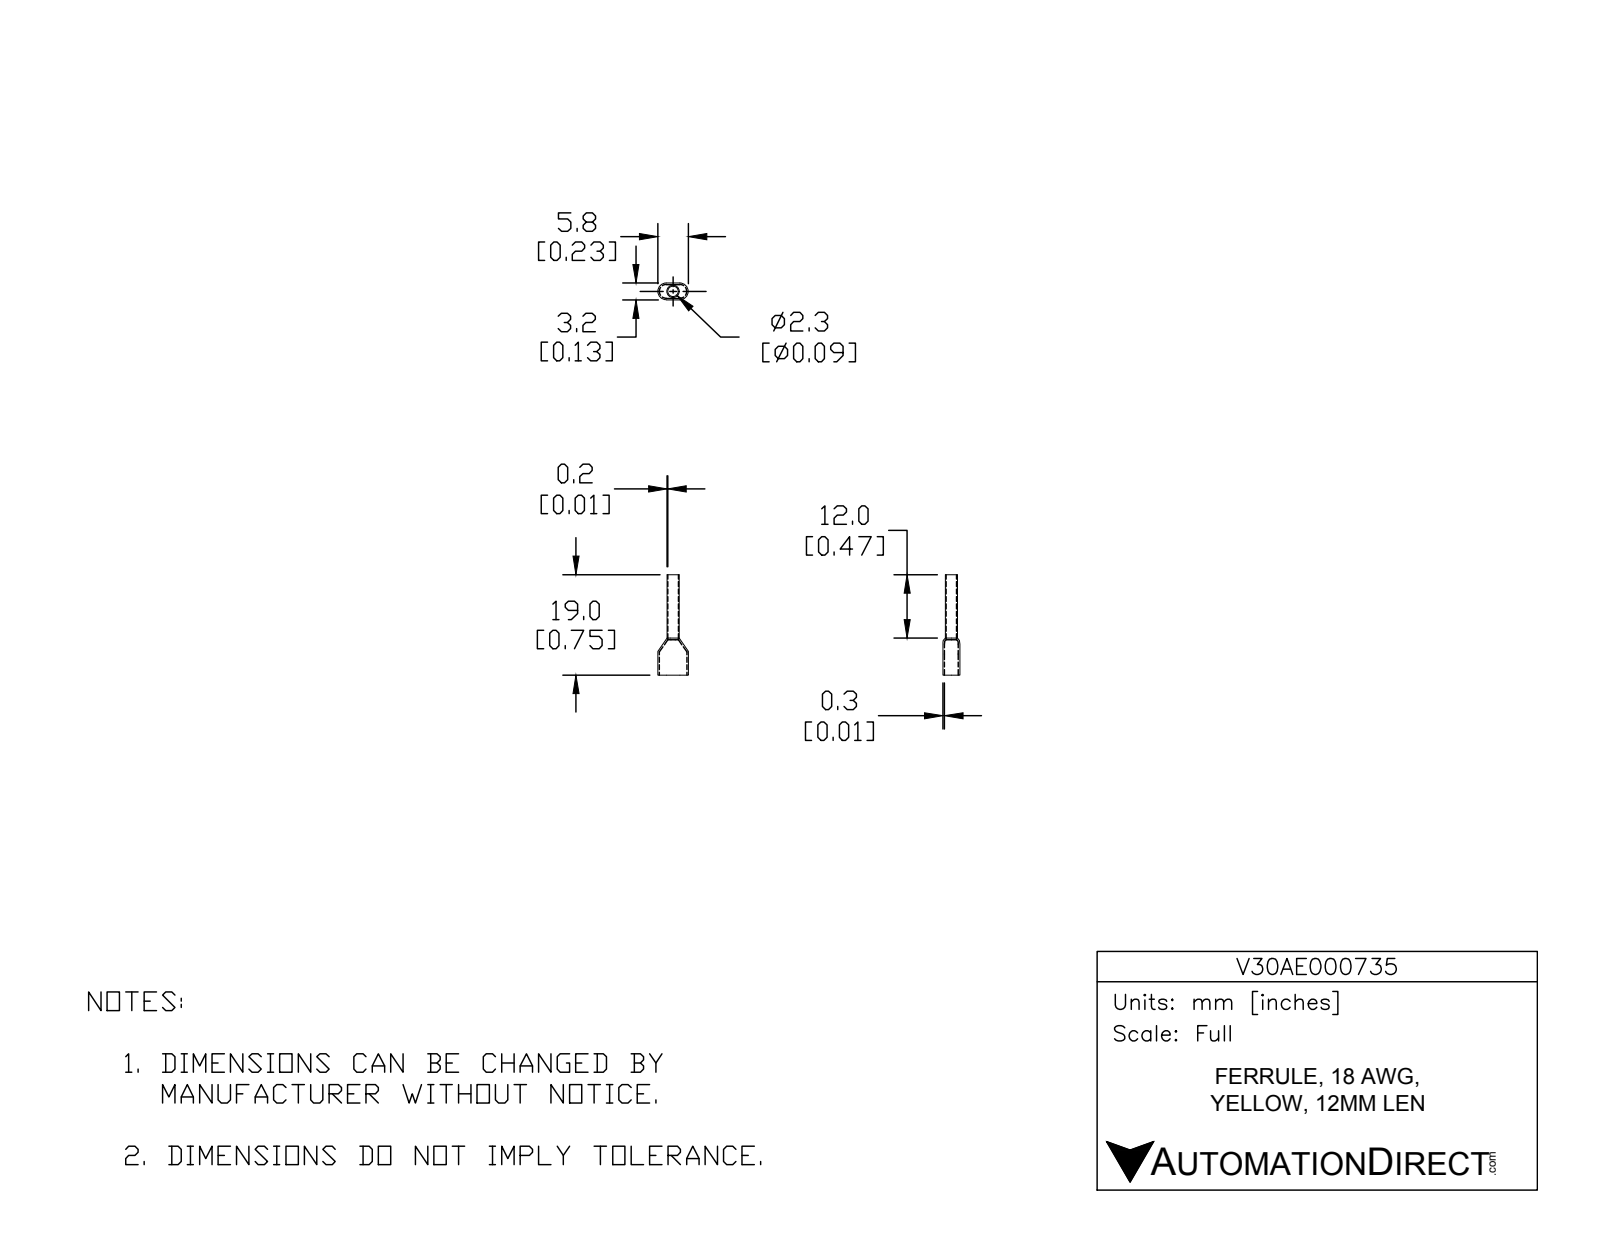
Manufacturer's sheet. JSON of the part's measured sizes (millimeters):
{"part_name": "V30AE000735", "step_written_by": "SolidWorks 2017 (AUTOMOTIVE_DESIGN)", "units": "millimeters", "bodies": {"solids": 2, "faces": 36, "planar": 14, "cylindrical": 22, "other": 0}, "overall_size": [19, 5.8, 3.2], "volume_mm3": 40, "surface_area_mm2": 356, "round_holes": [[2, 1]], "round_bosses_or_shafts": [[2.3, 1]], "partial_cylinders_radius": [[1.3, 5], [1.6, 5]], "face_to_face_distances": [2.9, 2.6, 3.2, 7, 19, 12, 6.7, 12.3]}
